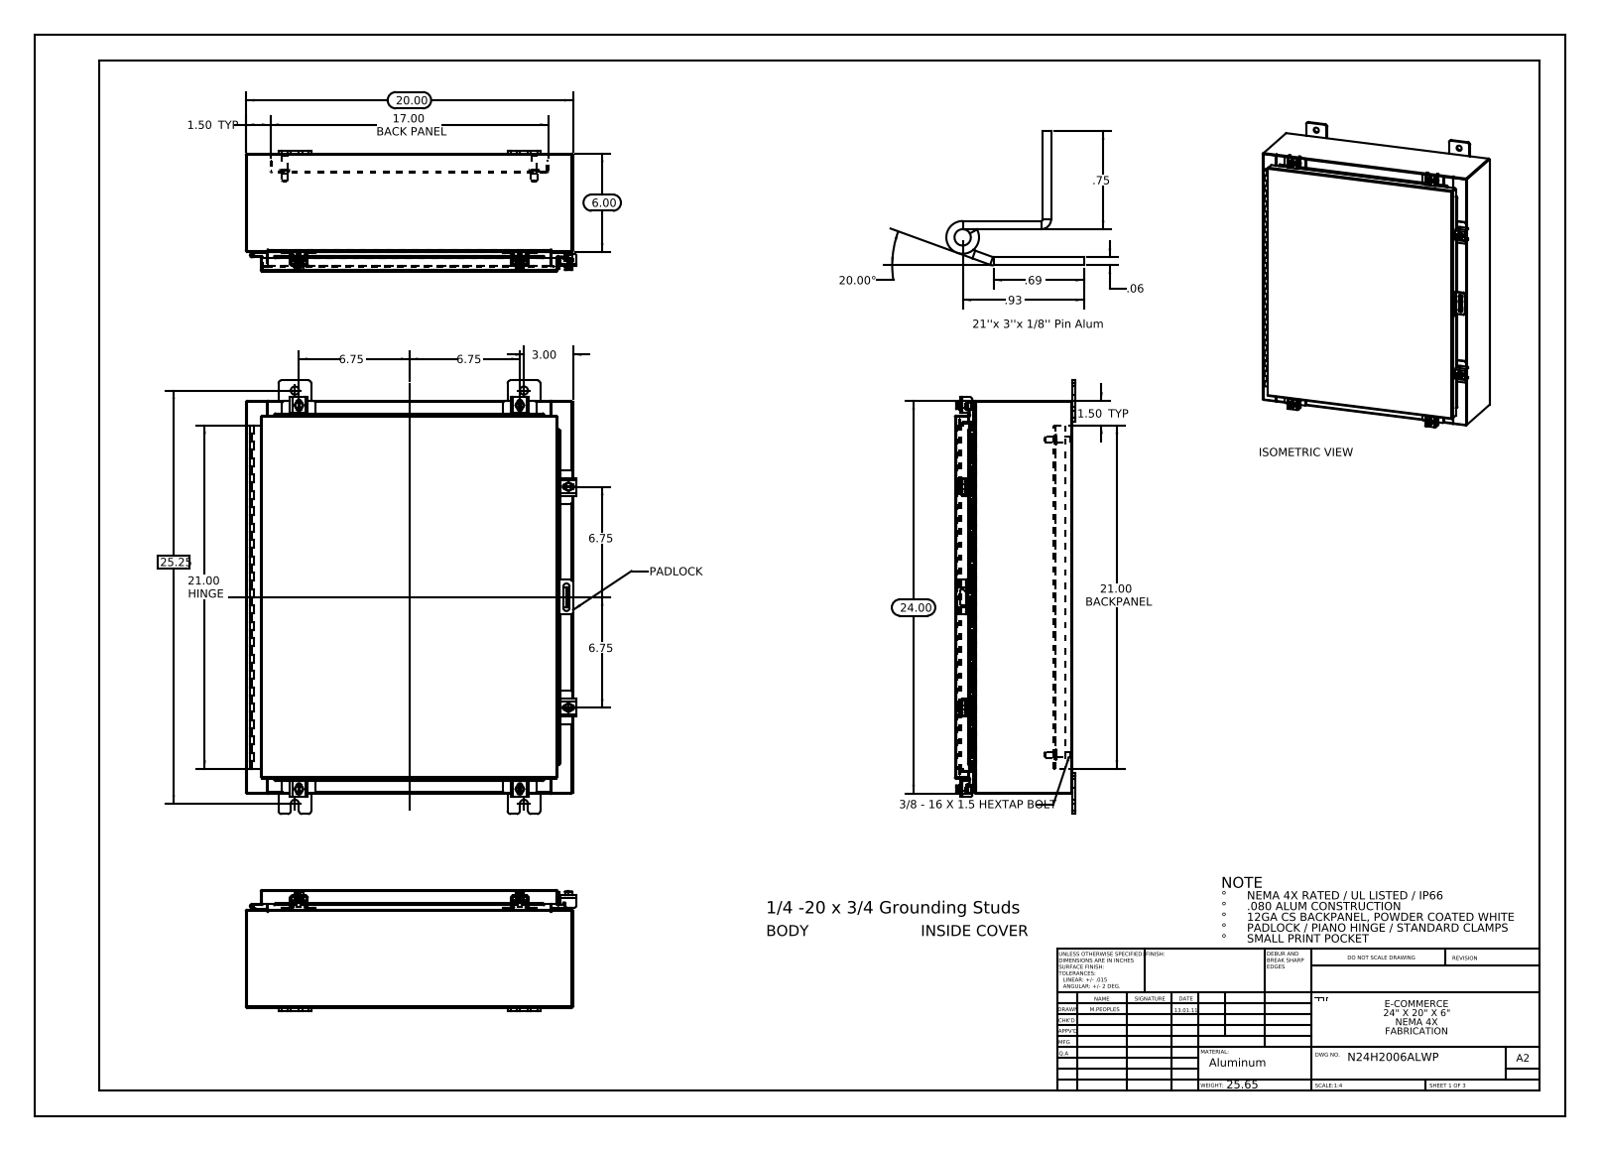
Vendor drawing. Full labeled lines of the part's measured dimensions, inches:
Part name (STEP PRODUCT): N24H2006ALWP Hinge Cover Side; N24H2006ALWP Top; N24H2006ALWP 125 Pin Hinge; N24H2006ALWP Mounting Feet (+8 more)
STEP written by: SolidWorks 2013 (CONFIG_CONTROL_DESIGN)
Units: inches
Bodies: 47 solids, 1709 faces (908 planar, 705 cylindrical, 96 other)
Overall size (bounding box): 26.5 × 20.211 × 7.389
Volume: 173.9 in³ · Surface area: 4 361 in²
Round holes (diameter × count): ⌀0.5 ×8, ⌀0.213 ×6, ⌀0.26 ×6, ⌀0.125 ×2, ⌀0.125 ×1
Round bosses / shafts (diameter × count): ⌀0.25 ×7, ⌀0.5 ×6, ⌀0.399 ×6, ⌀0.625 ×4, ⌀0.375 ×4, ⌀0.33 ×4
Partial cylindrical surfaces — rounded edges, fillets, slot ends (radius × count): R0.06 ×30, R0.013 ×25, R0.19 ×24, R0.088 ×21, R0.12 ×12, R0.141 ×12, R0.125 ×10, R0.05 ×9
Main face-to-face distances: 0.075, 7.126, 7.201, 7.051, 0.104, 1, 1.075, 6.051, 6.126, 1.179
Hole centre spacings: 21.369, 25.739, 13.5, 0.431, 0.934, 1.858, 2.275, 2.276
